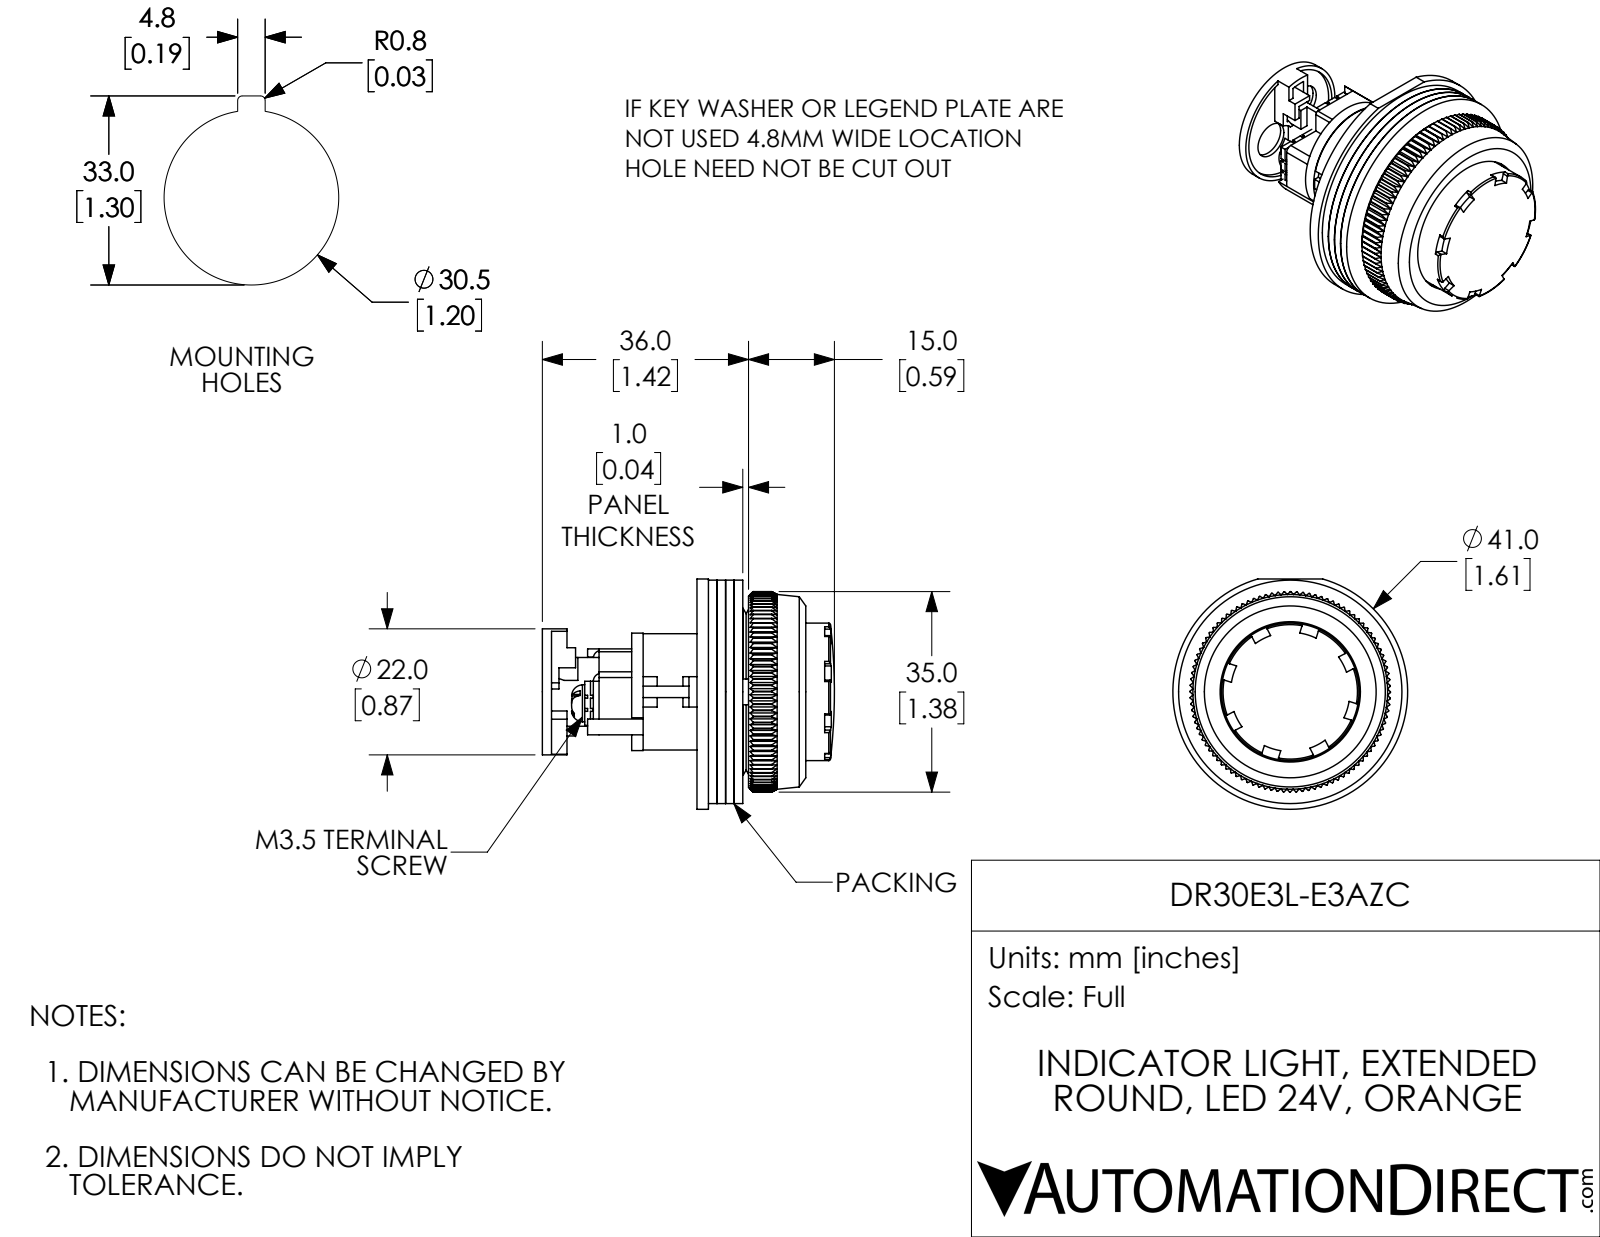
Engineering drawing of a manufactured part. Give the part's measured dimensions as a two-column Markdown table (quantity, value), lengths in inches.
| quantity | value |
| --- | --- |
| part name | DR30E3L-E3AZC |
| STEP written by | SolidWorks 2017 (AUTOMOTIVE_DESIGN) |
| units | inches |
| bodies | 16 solids, 1287 faces (717 planar, 328 cylindrical, 242 other) |
| overall size | 2.008 × 1.614 × 1.583 |
| volume | 1.072 in³ |
| surface area | 37.55 in² |
| round holes (diameter × count) | 0.118 × 2, 0.138 × 2, 0.252 × 2, 0.563 × 1, 0.63 × 1, 0.72 × 1, 0.787 × 1, 0.807 × 1, 0.866 × 1, 0.965 × 1, 1.122 × 1, 1.173 × 1 |
| round bosses / shafts (diameter × count) | 0.063 × 2, 1.614 × 1, 1.535 × 1, 1.16 × 1, 0.945 × 1, 0.858 × 1, 0.819 × 1, 0.799 × 1 |
| partial cylindrical surfaces (radius × count) | 0.012 × 16, 0.059 × 8, 0.01 × 5, 0.022 × 5, 0.016 × 4, 0.055 × 4, 0.02 × 2, 0.039 × 2 |
| main face-to-face distances | 0.059, 0.118, 0.177, 0.039, 0.197, 0.079, 0.315, 0.256, 0.098, 0.236 |
| hole center spacings | 0.176, 0.185, 0.361, 0.352, 0.37 |
